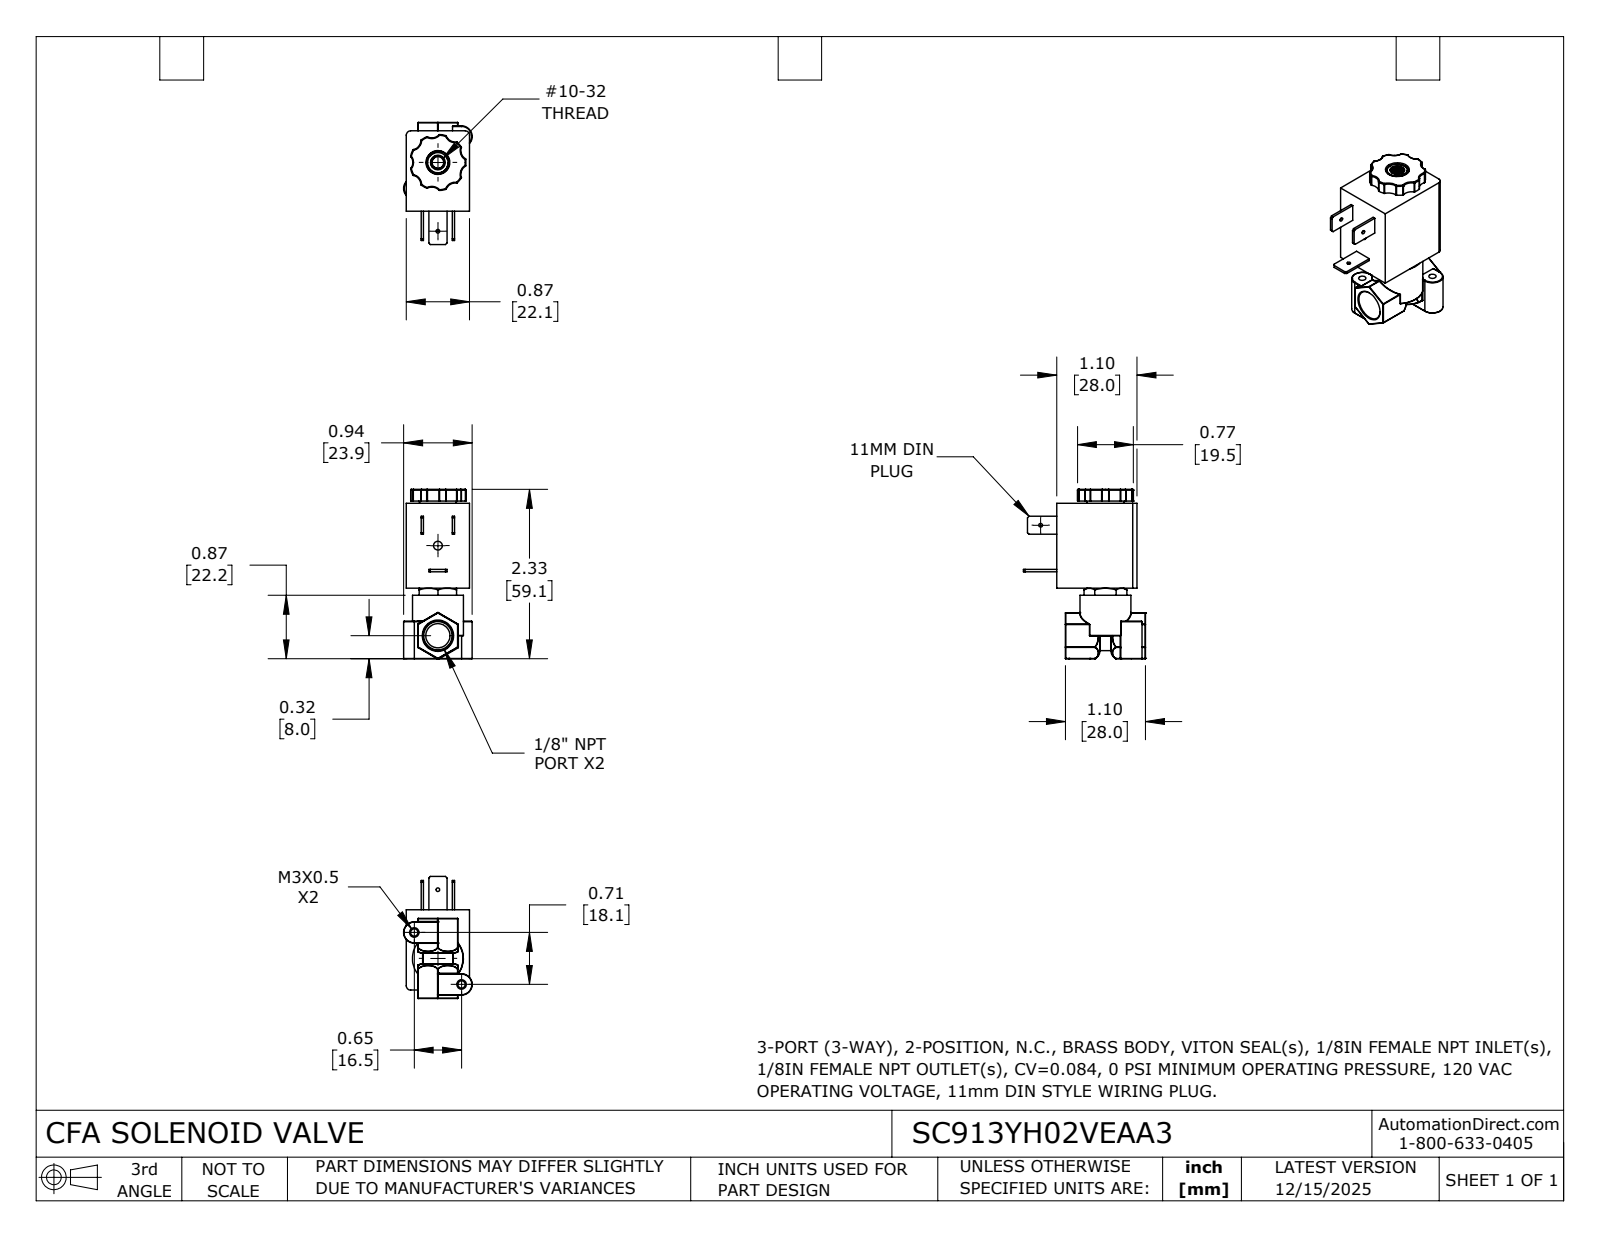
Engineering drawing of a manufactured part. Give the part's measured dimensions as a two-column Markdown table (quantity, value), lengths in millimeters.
| quantity | value |
| --- | --- |
| part name | SC913YH02VEAA3 |
| STEP written by | SolidWorks 2024 (CONFIG_CONTROL_DESIGN) |
| units | millimeters |
| bodies | 1 solid, 363 faces (70 planar, 142 cylindrical, 151 other) |
| overall size | 59.1 × 42.6 × 23.9 |
| volume | 25 780 mm³ |
| surface area | 8 955 mm² |
| round holes (diameter × count) | 1.3 × 2, 2.5 × 2, 3 × 1, 4.1 × 1, 8.3 × 1, 8.4 × 1 |
| round bosses / shafts (diameter × count) | 17.8 × 1, 8 × 1 |
| partial cylindrical surfaces (radius × count) | 0.1 × 29, 0.3 × 18, 0.2 × 12, 3.4 × 7, 0.4 × 2, 1.5 × 2, 3.4 × 2, 3.7 × 2 |
| main face-to-face distances | 22.1, 28, 29.6, 13.9, 34.5, 4.8, 4.1, 18, 24.7, 54.3 |
| hole center spacings | 12.3, 17.1, 24, 24.5, 31.4, 34.1 |
